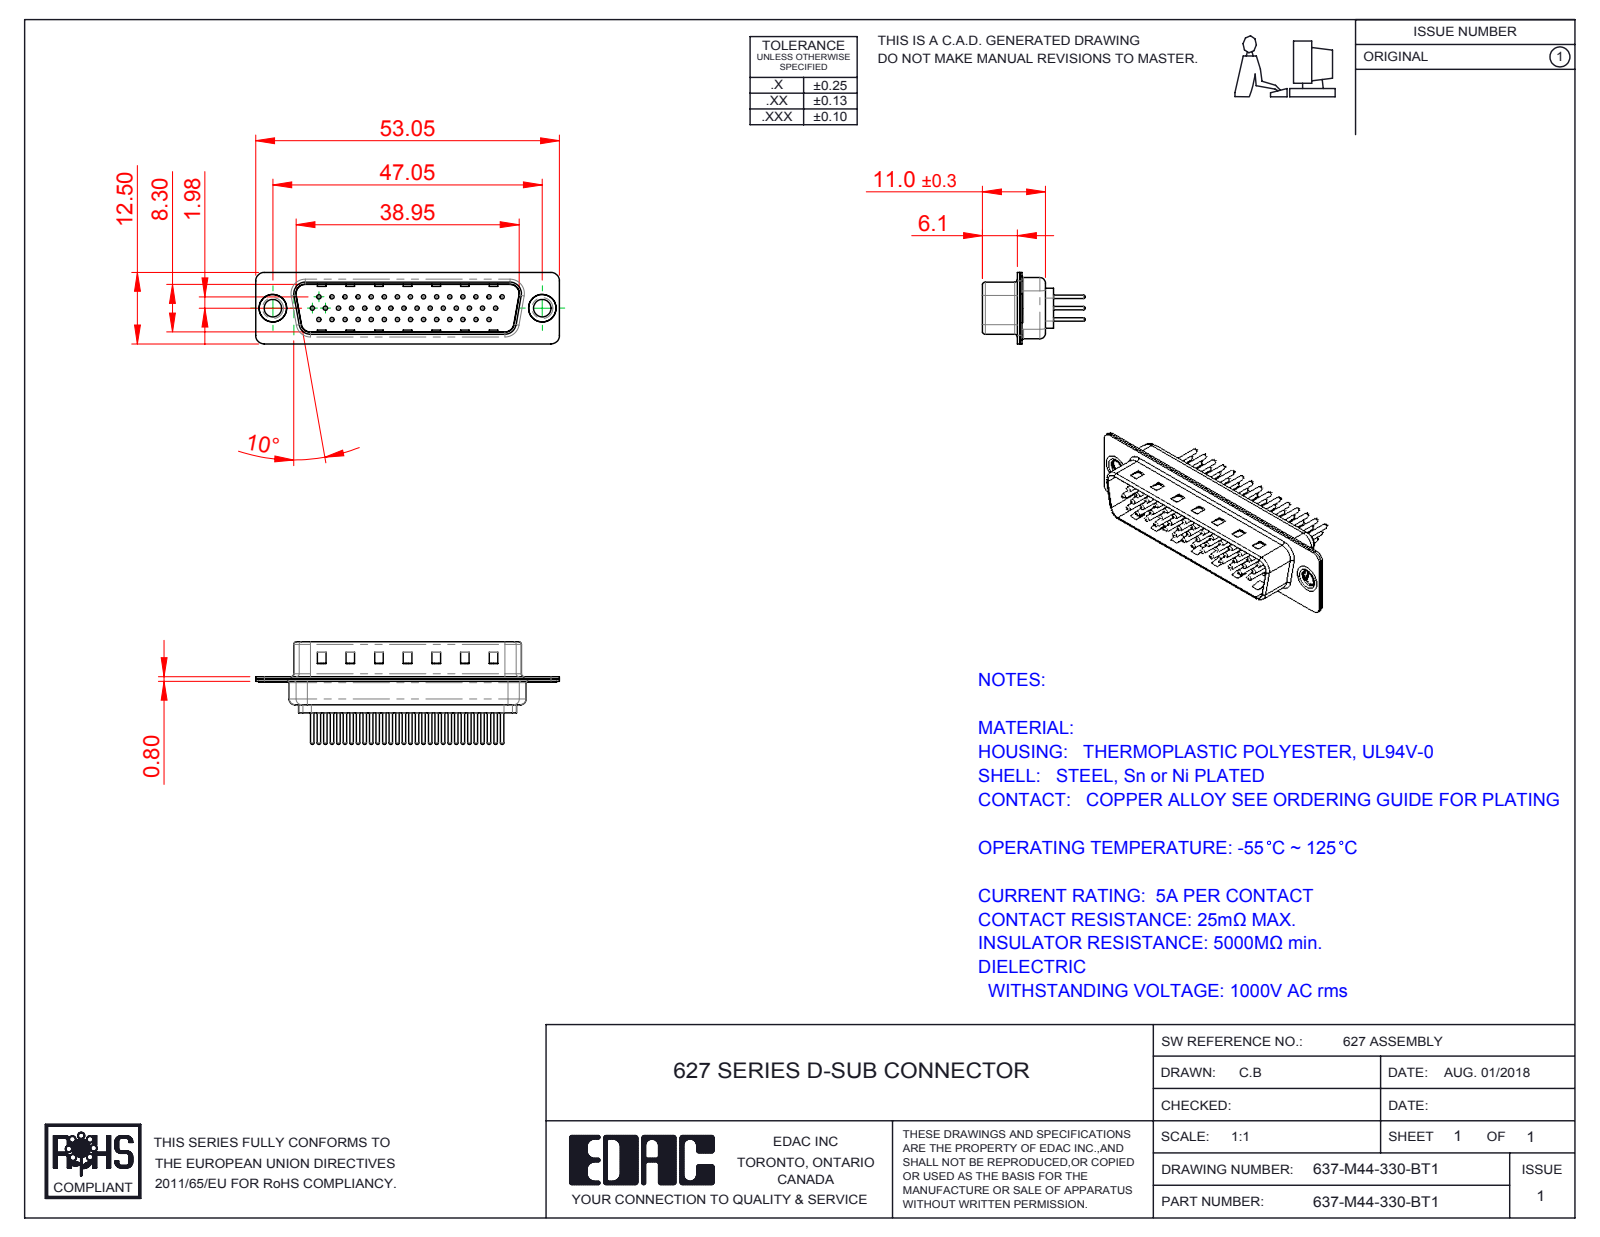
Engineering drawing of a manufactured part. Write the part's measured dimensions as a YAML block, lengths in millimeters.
part_name: "637M Contact Row 1_30; 637M Housing_44 Contacts; 637M Contact Row 2_30; 637M Shell Rear_44 Contacts (+4 more)"
step_written_by: "SolidWorks 2016 (CONFIG_CONTROL_DESIGN)"
units: millimeters
bodies: {solids: 49, faces: 1978, planar: 479, cylindrical: 737, other: 762}
overall_size: [53.05, 17.9, 12.5]
volume: 2750
surface_area: 8321
round_holes:
  - {diameter: 0.75, count: 44}
  - {diameter: 1.6, count: 44}
  - {diameter: 2, count: 44}
  - {diameter: 3.05, count: 2}
  - {diameter: 4, count: 2}
  - {diameter: 4.8, count: 2}
round_bosses_or_shafts:
  - {diameter: 1.5, count: 44}
  - {diameter: 0.6, count: 44}
  - {diameter: 2, count: 3}
  - {diameter: 0.75, count: 3}
  - {diameter: 5, count: 2}
  - {diameter: 4.9, count: 2}
  - {diameter: 3.55, count: 2}
partial_cylinders:
  - {radius: 1.5, count: 16}
  - {radius: 2, count: 12}
  - {radius: 0.5, count: 8}
  - {radius: 1.6, count: 8}
  - {radius: 0.25, count: 4}
  - {radius: 0.6, count: 4}
  - {radius: 0.65, count: 4}
  - {radius: 0.9, count: 4}
face_to_face_distances: [0.4, 0.8, 9.5, 9.1, 8.7, 9.9, 0.75, 1.1, 0.35, 5.9]
hole_center_spacings: [2.28, 3.96, 2.29, 4.57, 8.24, 6.86, 11.43, 14.99]
